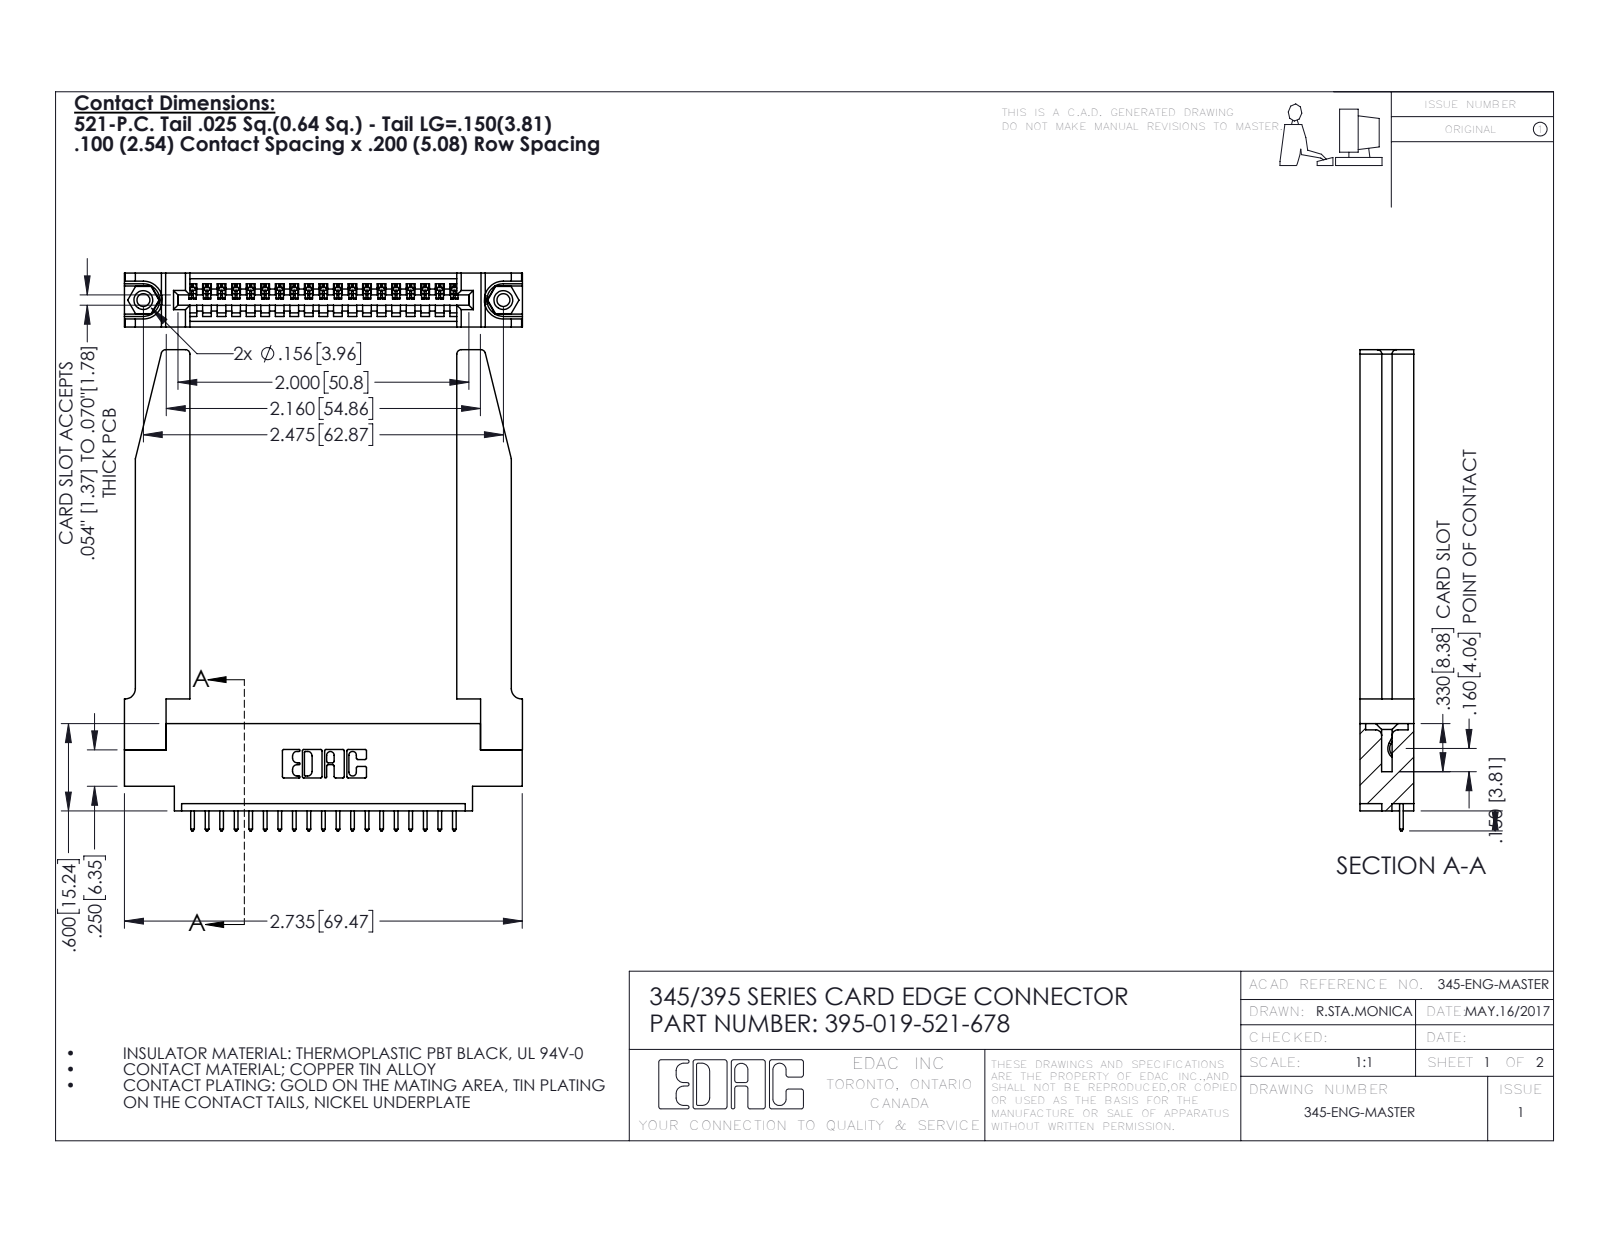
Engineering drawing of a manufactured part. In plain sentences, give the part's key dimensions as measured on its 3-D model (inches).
The part is named "345-220-078_345-220-078; 345-292-001_345-293-121; 345 Part_0.170 Offset - 0.156 Dia-TH; 345-250-001_345-250-001-102 (+1 more)". Its 3-D file was written by "SolidWorks 2016 (CONFIG_CONTROL_DESIGN)". It is 24 solids with 1466 faces: 986 planar, 428 cylindrical and 52 other. Overall it measures 3.307 by 2.736 by 0.37 inches. Its volume is 0.855 cubic inches and its surface area 22.86 square inches. Round holes: 2 of diameter 0.089, 2 of diameter 0.125, 2 of diameter 0.156, 1 of diameter 0.064. Round bosses or shafts: 2 of diameter 0.155. Partial cylindrical surfaces (rounded edges, fillets, slot ends): 38 of radius 0.006, 38 of radius 0.01, 22 of radius 0.01, 8 of radius 0.03, 6 of radius 0.007, 6 of radius 0.031, 3 of radius 0.026, 2 of radius 0.031. The main face-to-face distances are 0.37, 0.072, 0.298, 0.148, 0.15, 0.2, 0.098, 0.272, 0.025, 0.22. The hole center spacings are 0.27, 2.241, 2.475.
